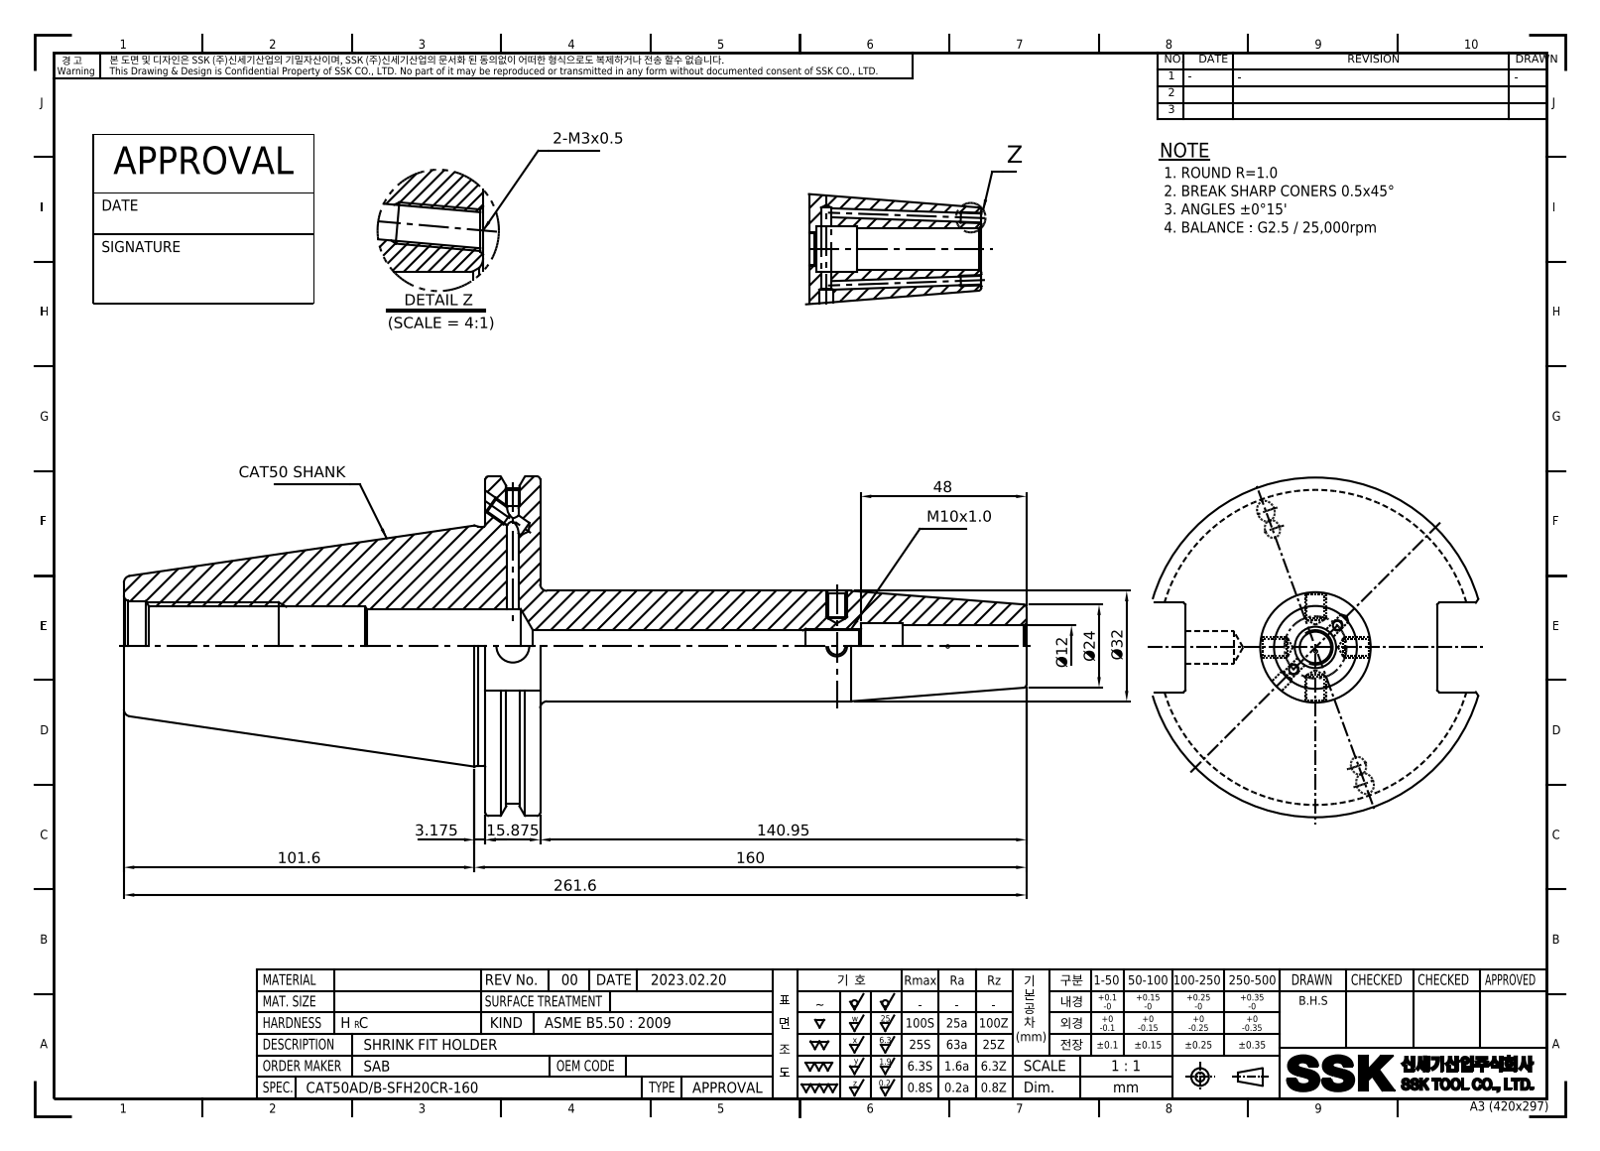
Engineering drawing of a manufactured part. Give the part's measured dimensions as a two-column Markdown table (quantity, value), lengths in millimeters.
| quantity | value |
| --- | --- |
| part name | CAT50ADB-SFH12CR-160 |
| STEP written by | Autodesk Inventor 2022 (AUTOMOTIVE_DESIGN) |
| units | millimeters |
| bodies | 1 solid, 89 faces (37 planar, 29 cylindrical, 23 other) |
| overall size | 261.6 × 98.42 × 94.69 |
| volume | 411 998 mm³ |
| surface area | 63 238 mm² |
| round holes (diameter × count) | 2.46 × 2, 3.24 × 2, 4.13 × 2, 4.2 × 2, 5 × 2, 8.92 × 1, 9.53 × 1, 12 × 1, 13.2 × 1, 21.5 × 1, 21.97 × 1, 26.2 × 1 |
| round bosses / shafts (diameter × count) | 98.42 × 1, 91.29 × 1, 69.25 × 1, 32 × 1 |
| main face-to-face distances | 15.88, 104.77, 120.65, 73.03, 25.9, 261.6, 156.83, 140.95, 110.82, 6.05 |
